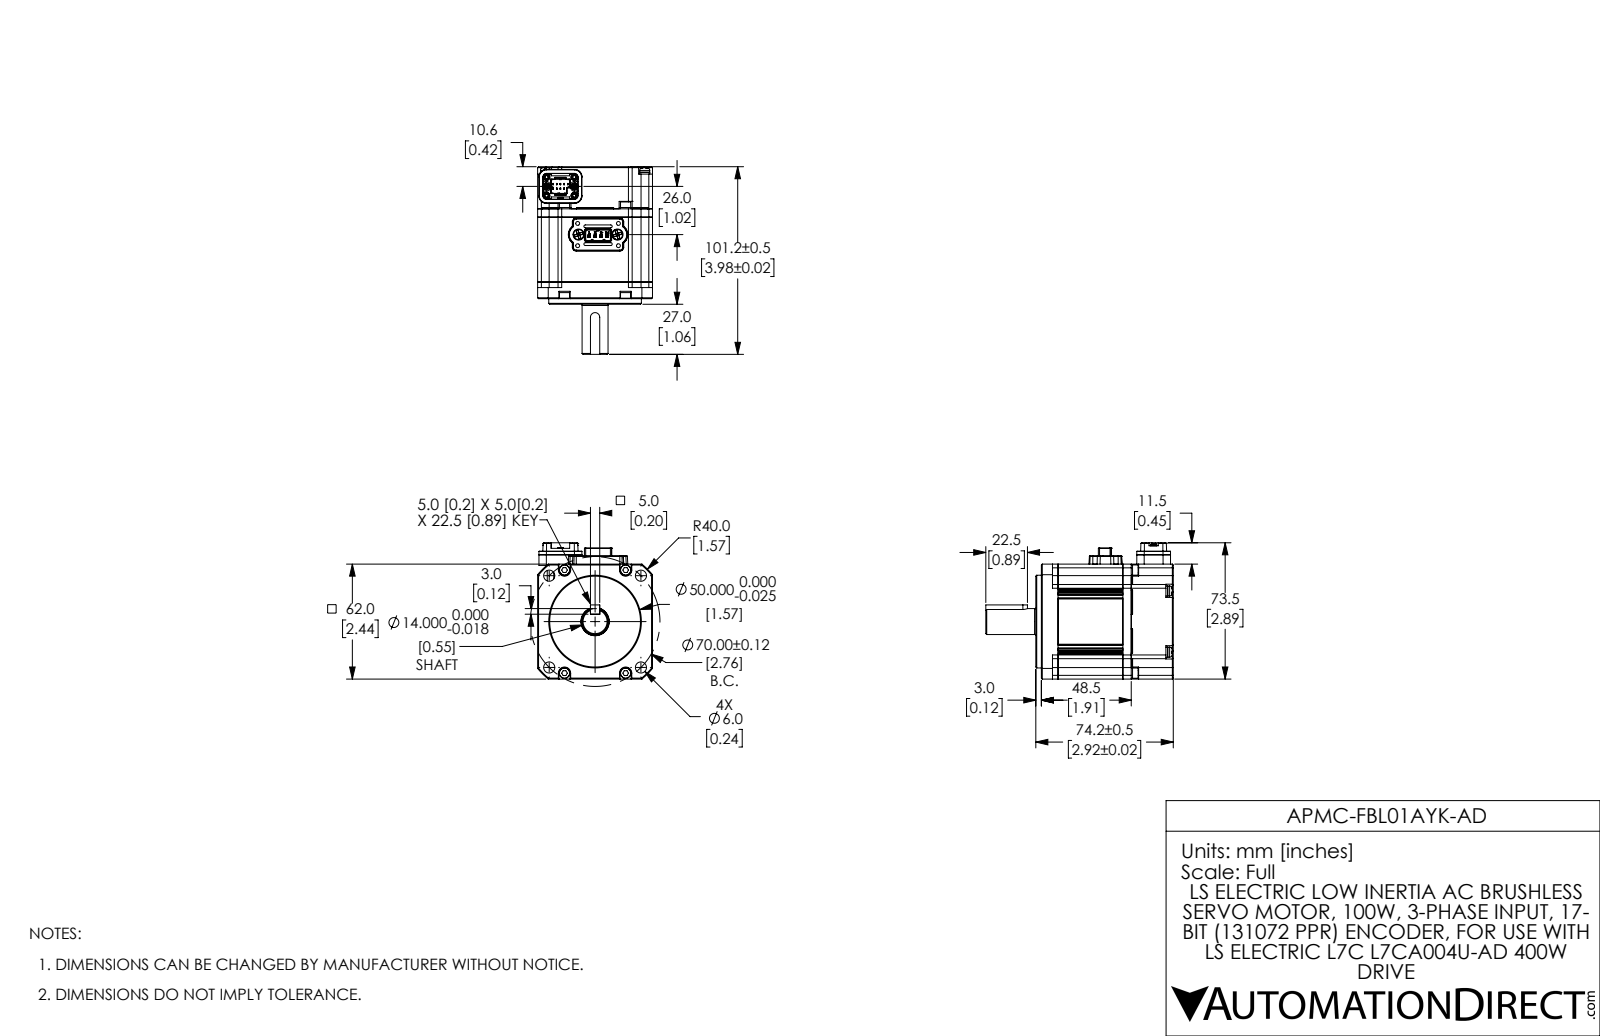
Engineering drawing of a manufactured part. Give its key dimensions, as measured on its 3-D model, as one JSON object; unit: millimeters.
{"part_name": "APMC-FBL01AYK-AD", "step_written_by": "SolidWorks 2017 (AUTOMOTIVE_DESIGN)", "units": "millimeters", "bodies": {"solids": 45, "faces": 1853, "planar": 1196, "cylindrical": 478, "other": 179}, "overall_size": [101.2, 73.5, 62], "volume_mm3": 254700, "surface_area_mm2": 68130, "round_holes": [[2.1, 10], [3, 10], [3.5, 8], [1.6, 6], [6, 6], [3.1, 4], [3.3, 1], [3.4, 1], [15.3, 1]], "round_bosses_or_shafts": [[5.4, 6], [5.6, 4], [5.5, 4], [2.2, 2], [50, 1], [15, 1], [14.8, 1], [14, 1]], "partial_cylinders_radius": [[0.2, 20], [0.3, 20], [3, 12], [1, 10], [0.2, 9], [2, 8], [0.5, 7], [0.1, 6]], "face_to_face_distances": [4.5, 35, 0.7, 5.2, 39.5, 40.2, 62, 9, 3, 22], "hole_center_spacings": [5, 6, 8.5, 8.8, 15.3, 16, 22.3, 31.5]}
